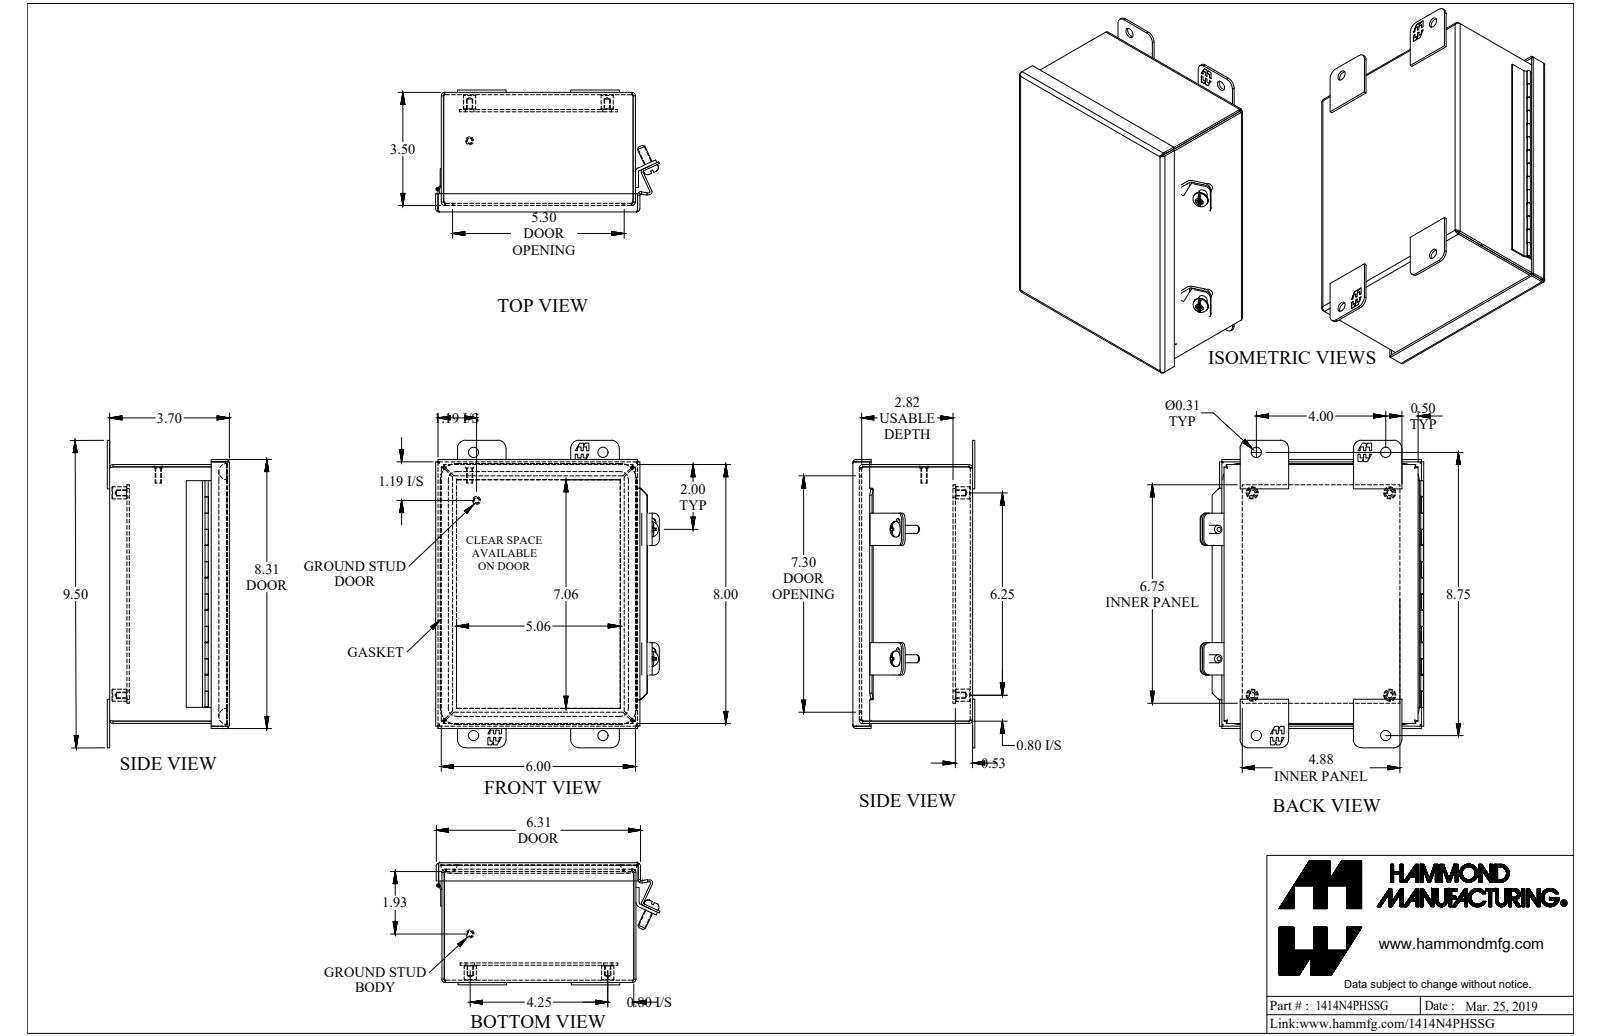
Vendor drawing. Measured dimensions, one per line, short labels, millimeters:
name: 1414N4PHSSG
written by: SolidWorks 2018 (AUTOMOTIVE_DESIGN)
unit: mm
bodies: 21 solids, 668 faces (432 planar, 172 cylindrical, 64 other)
size: 241.3 × 175.3 × 95.7
volume: 360 200 mm³; area: 400 700 mm²
holes: 4× ⌀4, 4× ⌀6.7, 4× ⌀8, 2× ⌀5.4, 1× ⌀1.3
bosses: 4× ⌀9.5, 4× ⌀6.4, 2× ⌀12.2, 2× ⌀4.8, 1× ⌀2.5, 1× ⌀1.1
rounds: 24× R6.4, 9× R0.9, 9× R2.7, 8× R4.8, 4× R0.2, 4× R0.3, 4× R1.2, 4× R2
face distances: 1.8, 92.1, 78.6, 13.5, 93.9, 150.6, 90.2, 15.3, 201.4, 80.4
hole spacings: 31.9, 190.5, 217.4, 158.8, 109.5, 192, 101.6, 108
